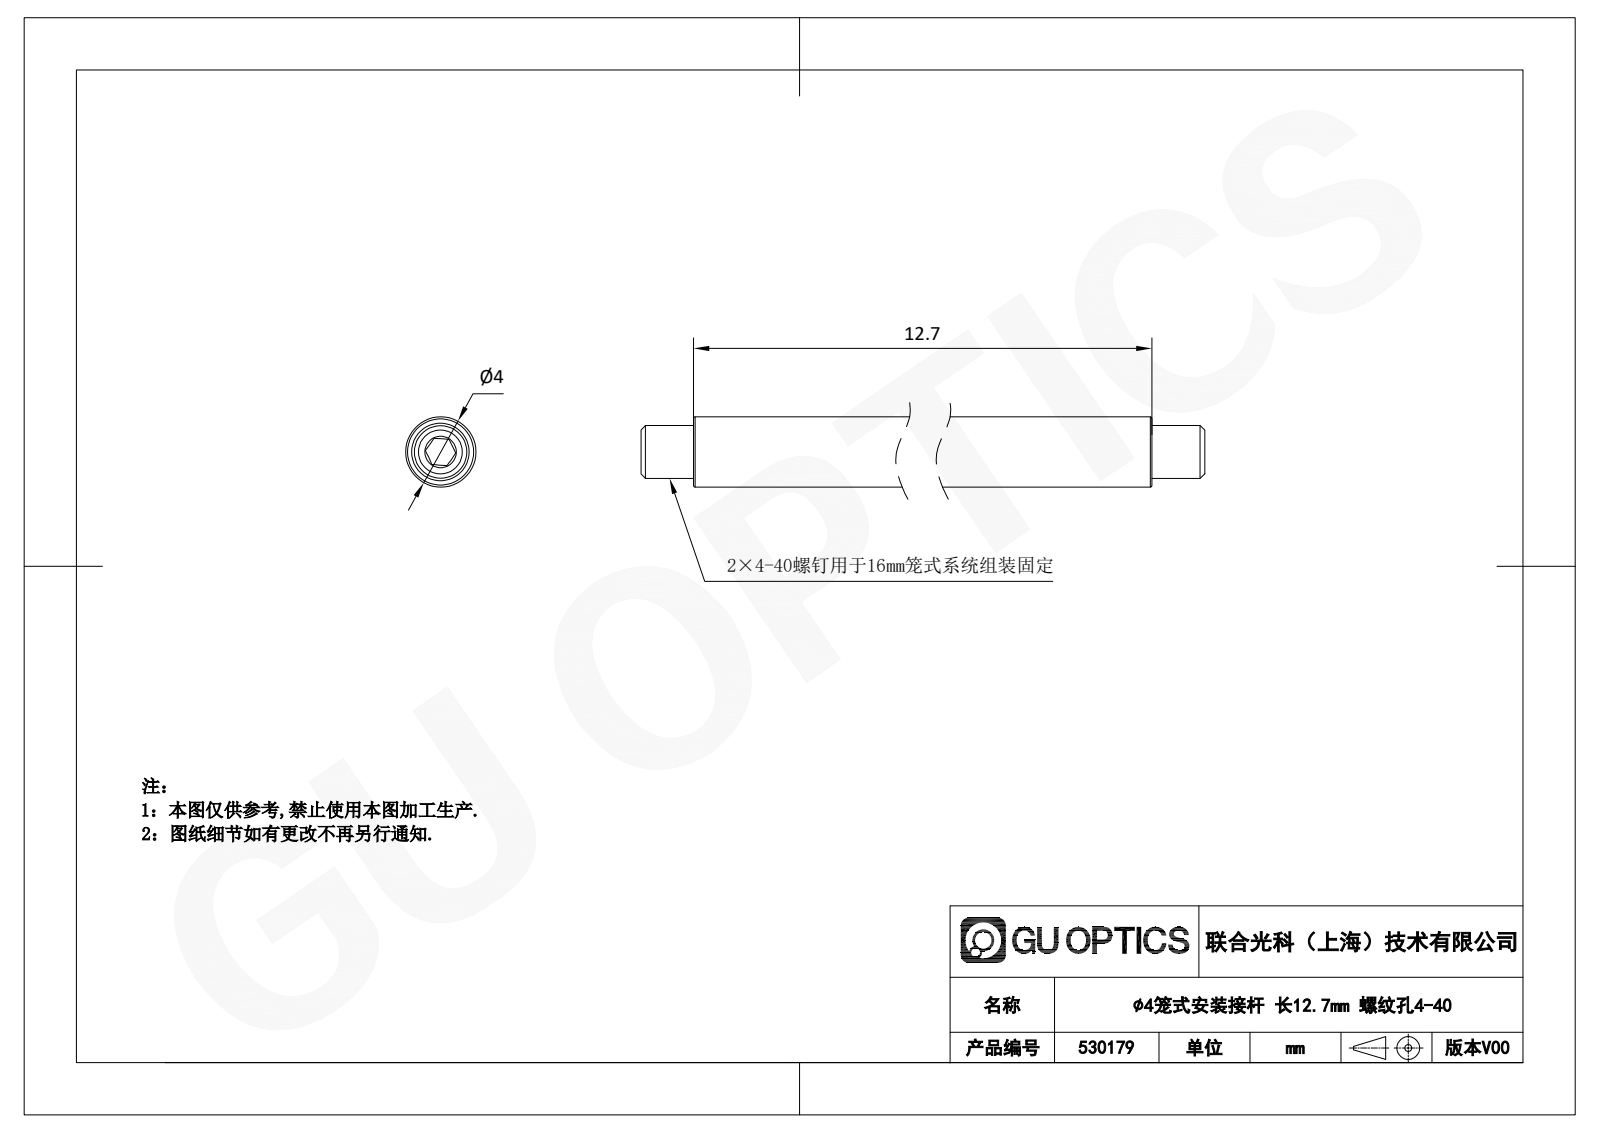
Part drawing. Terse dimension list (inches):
name: 530179
written by: SolidWorks 2020 (CONFIG_CONTROL_DESIGN)
unit: in
bodies: 3 solids, 37 faces (20 planar, 5 cylindrical, 12 other)
size: 0.894 × 0.157 × 0.157
volume: 0.013 in³; area: 0.696 in²
holes: 1× ⌀0.098
bosses: 1× ⌀0.157, 1× ⌀0.118
face distances: 0.118, 0.382, 0.197, 0.315, 0.579, 0.697, 0.059, 0.5, 0.039, 0.854
